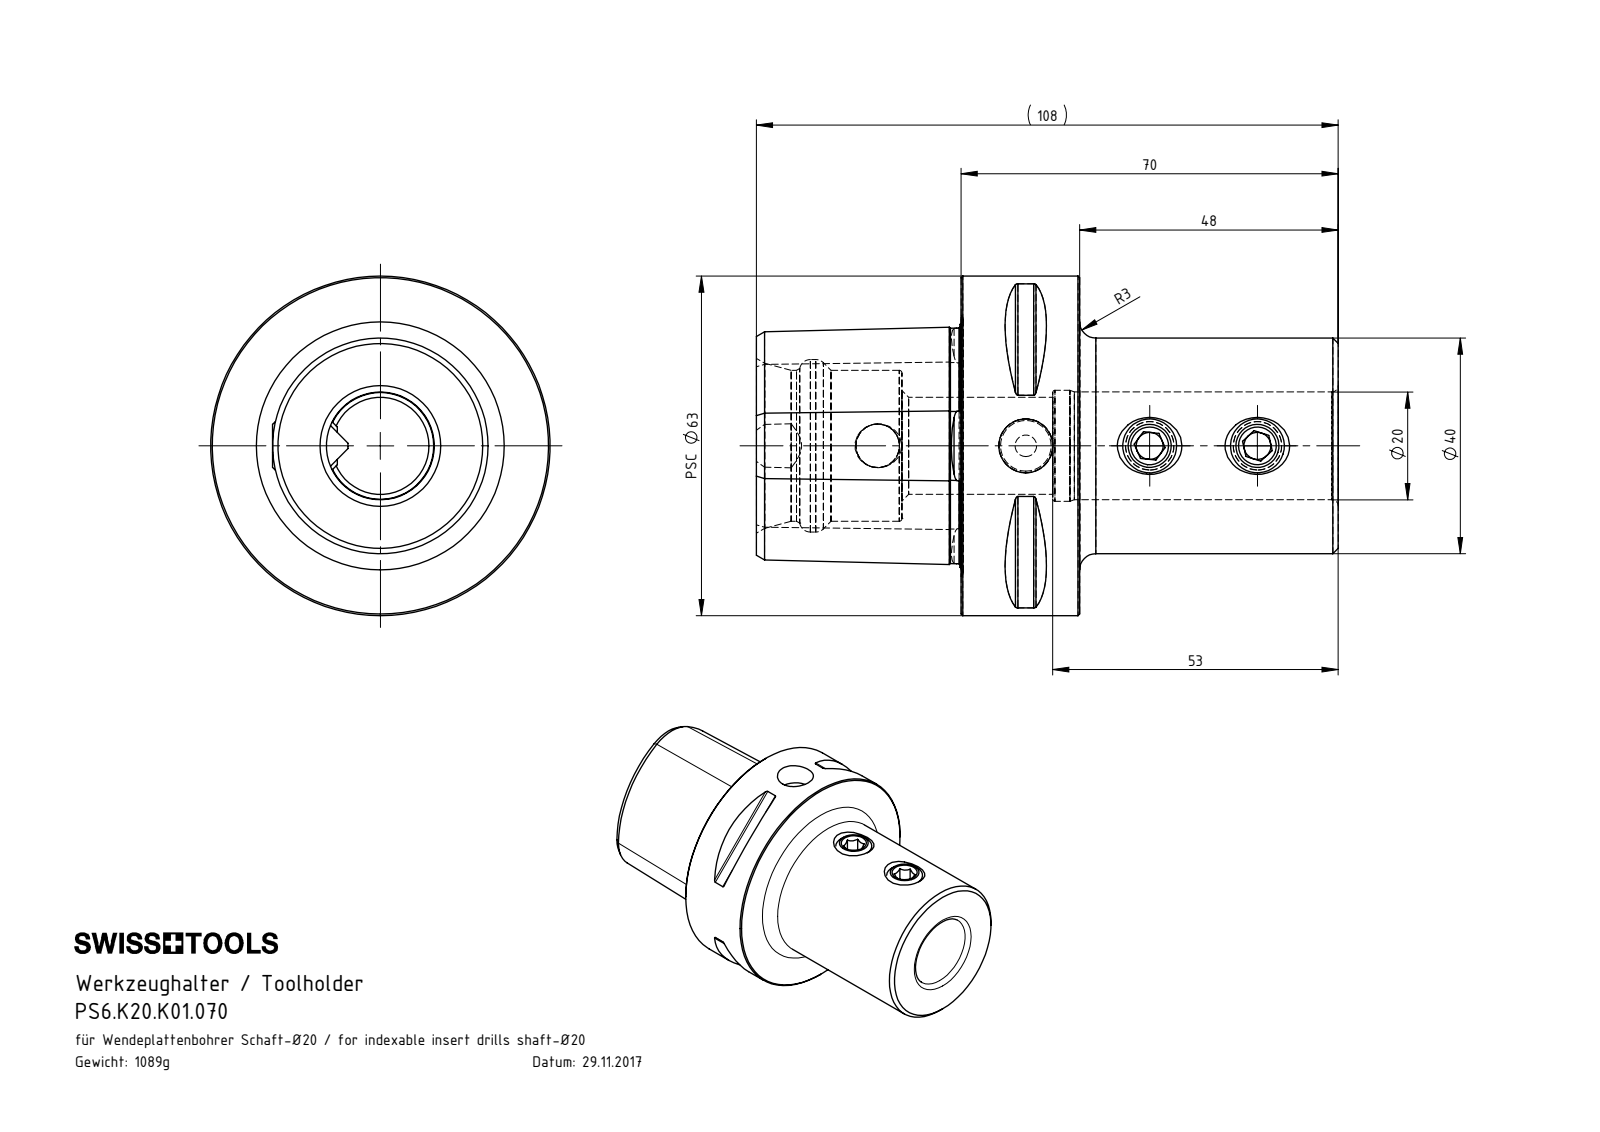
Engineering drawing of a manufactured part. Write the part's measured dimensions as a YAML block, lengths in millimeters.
part_name: "PS6.K20.K01.070; PS6-K20.K01.070_C; K20-ER2.010.014_PreviewCfg; K20-ER1.010.012_PreviewCfg"
step_written_by: "SolidWorks 2017 (AUTOMOTIVE_DESIGN)"
units: millimeters
bodies: {solids: 3, faces: 204, planar: 50, cylindrical: 45, other: 109}
overall_size: [108, 63, 63]
volume: 138947
surface_area: 30343
round_holes:
  - {diameter: 5, count: 2}
  - {diameter: 9, count: 2}
  - {diameter: 8.1, count: 1}
  - {diameter: 10, count: 1}
  - {diameter: 18, count: 1}
  - {diameter: 20, count: 1}
  - {diameter: 20.6, count: 1}
  - {diameter: 28, count: 1}
  - {diameter: 32, count: 1}
round_bosses_or_shafts:
  - {diameter: 10, count: 2}
  - {diameter: 63, count: 1}
  - {diameter: 40, count: 1}
partial_cylinders:
  - {radius: 0.5, count: 8}
  - {radius: 6, count: 1}
face_to_face_distances: [22, 70, 48, 38, 60, 108, 24.88, 27, 11, 33]
hole_center_spacings: [20, 23, 27.5, 43, 50.5, 70.5]
